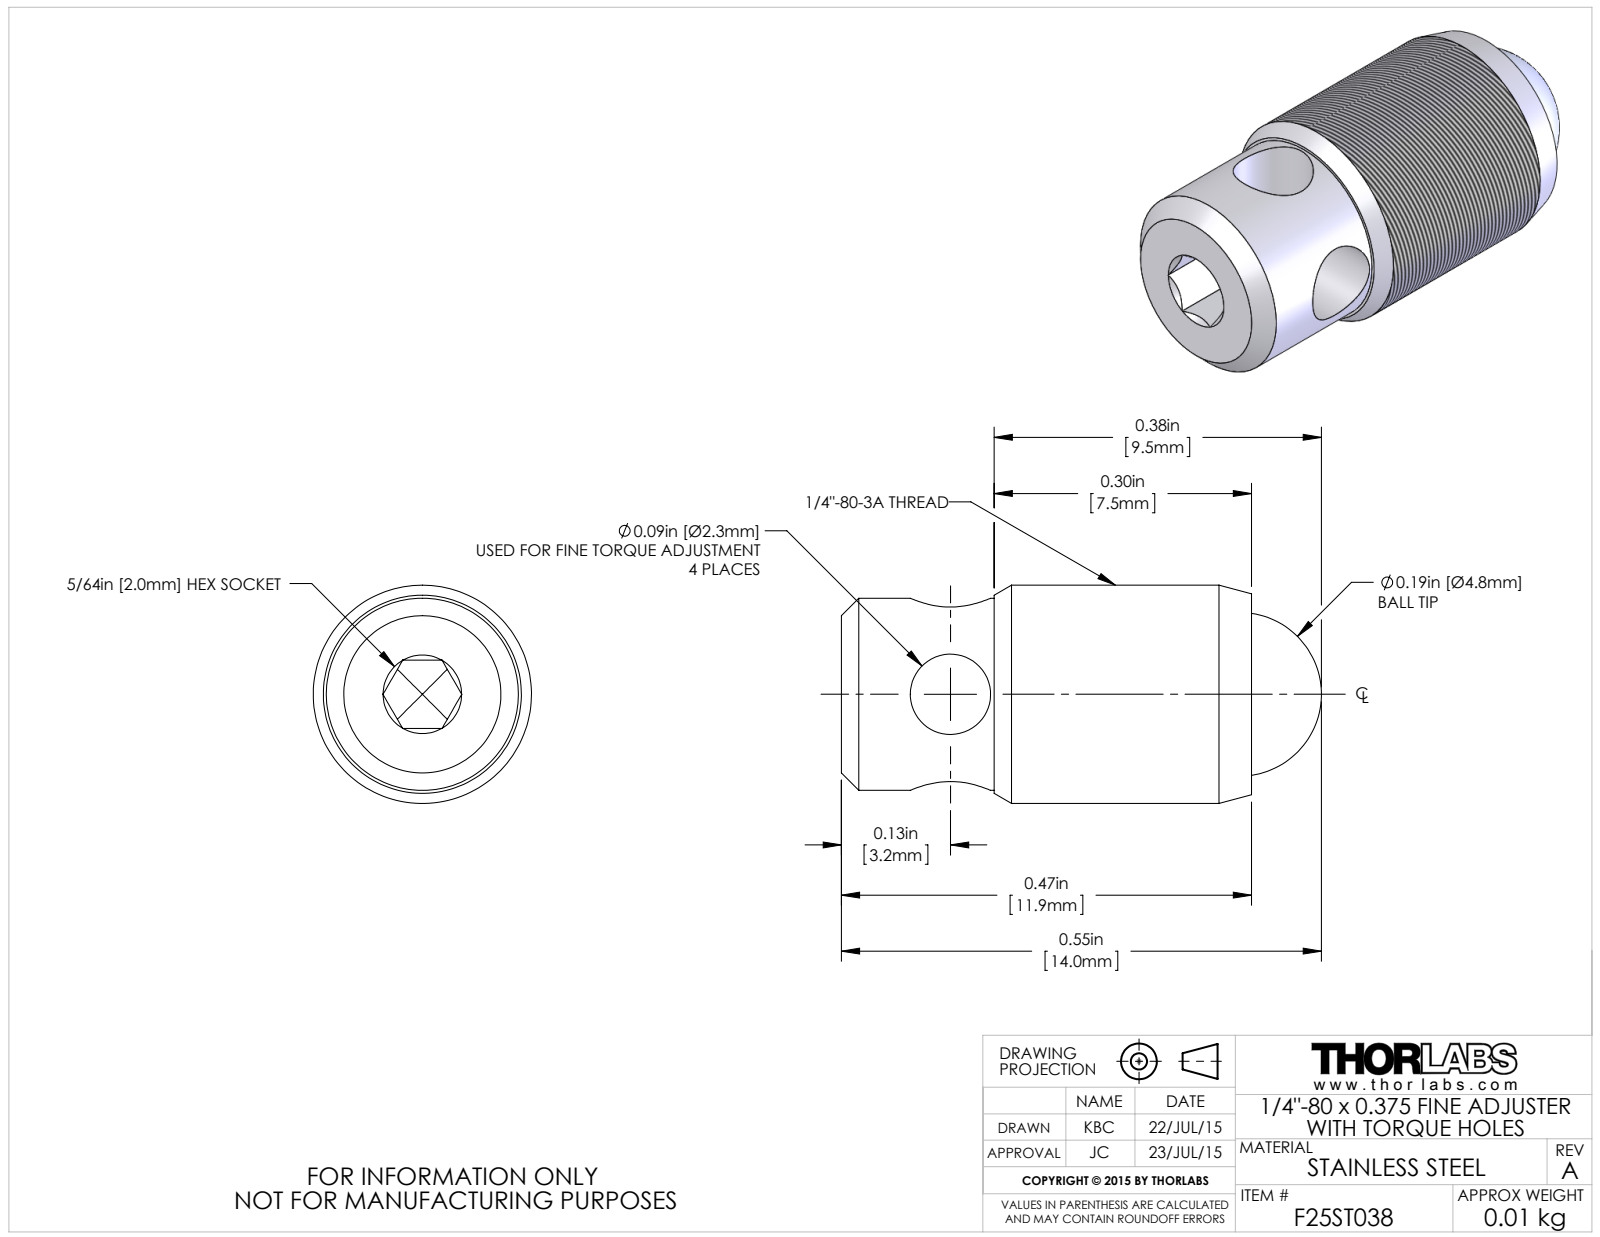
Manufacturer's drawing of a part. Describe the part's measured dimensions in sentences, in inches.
The part is named "TTN045067-E0W". Its 3-D file was written by "SolidWorks 2014 (AUTOMOTIVE_DESIGN)". It is 2 solids with 40 faces: 9 planar, 14 cylindrical and 17 other. Overall it measures 0.55 by 0.25 by 0.25 inches. Its volume is 0.019 cubic inches and its surface area 0.652 square inches. Round holes: 2 of diameter 0.092, 1 of diameter 0.188. Round bosses or shafts: 1 of diameter 0.25, 1 of diameter 0.22. The main face-to-face distances are 0.47, 0.078, 0.175, 0.295.
